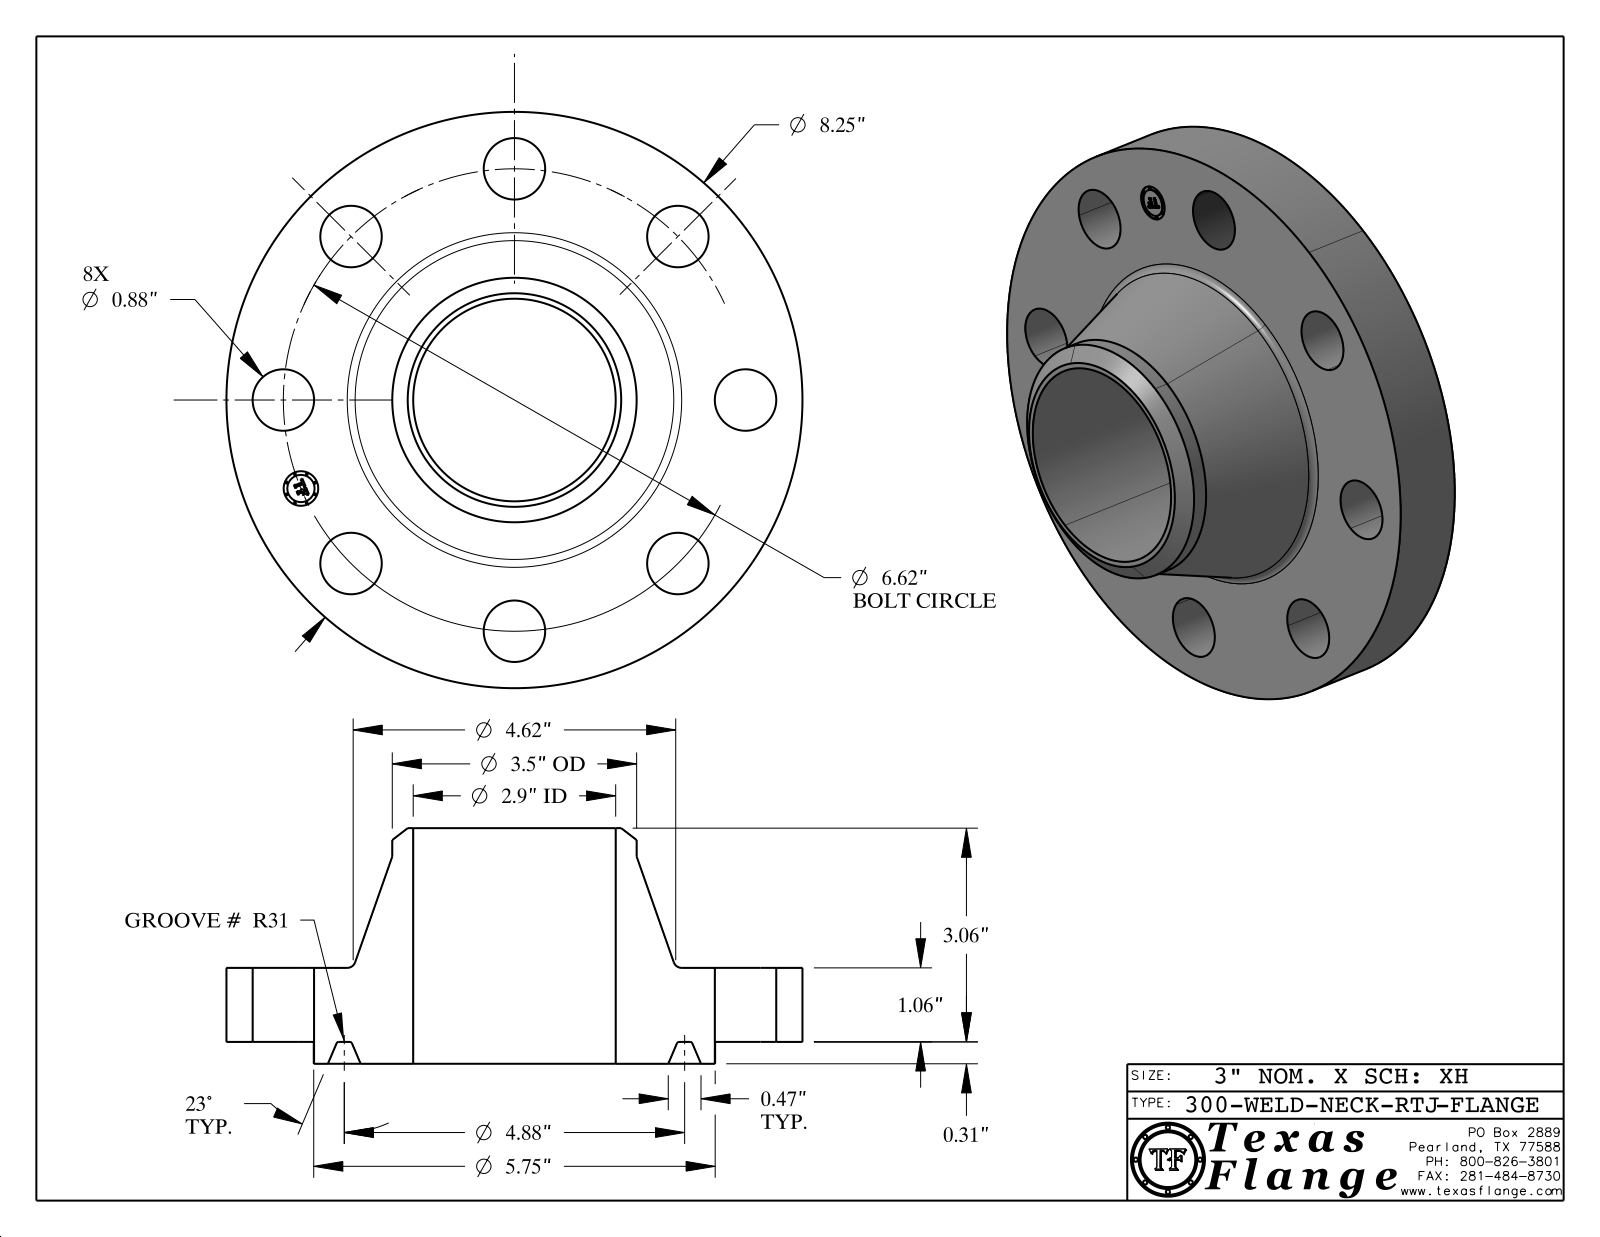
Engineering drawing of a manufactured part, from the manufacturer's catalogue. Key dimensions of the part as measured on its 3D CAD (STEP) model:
Part name (STEP PRODUCT): 300-WELD-NECK-RTJ
STEP written by: CATIA V5 STEP AP214 (AUTOMOTIVE_DESIGN)
Units: inches
Bodies: 1 solid, 437 faces (371 planar, 52 cylindrical, 14 other)
Overall size (bounding box): 8.25 × 8.25 × 3.373
Volume: 60.24 in³ · Surface area: 194.8 in²
Round holes (diameter × count): ⌀0.88 ×8, ⌀0.495 ×1, ⌀2.9 ×1
Round bosses / shafts (diameter × count): ⌀0.03 ×8, ⌀8.25 ×1, ⌀5.75 ×1, ⌀3.5 ×1, ⌀0.39 ×1
Main face-to-face distances: 1.06, 0.313, 1.373, 3.373, 3.06, 2, 0.015, 1.358, 1.045, 2.015
Hole centre spacings: 3.31, 2.533, 6.116, 4.681, 4.681, 1.291, 3.678, 6.493
